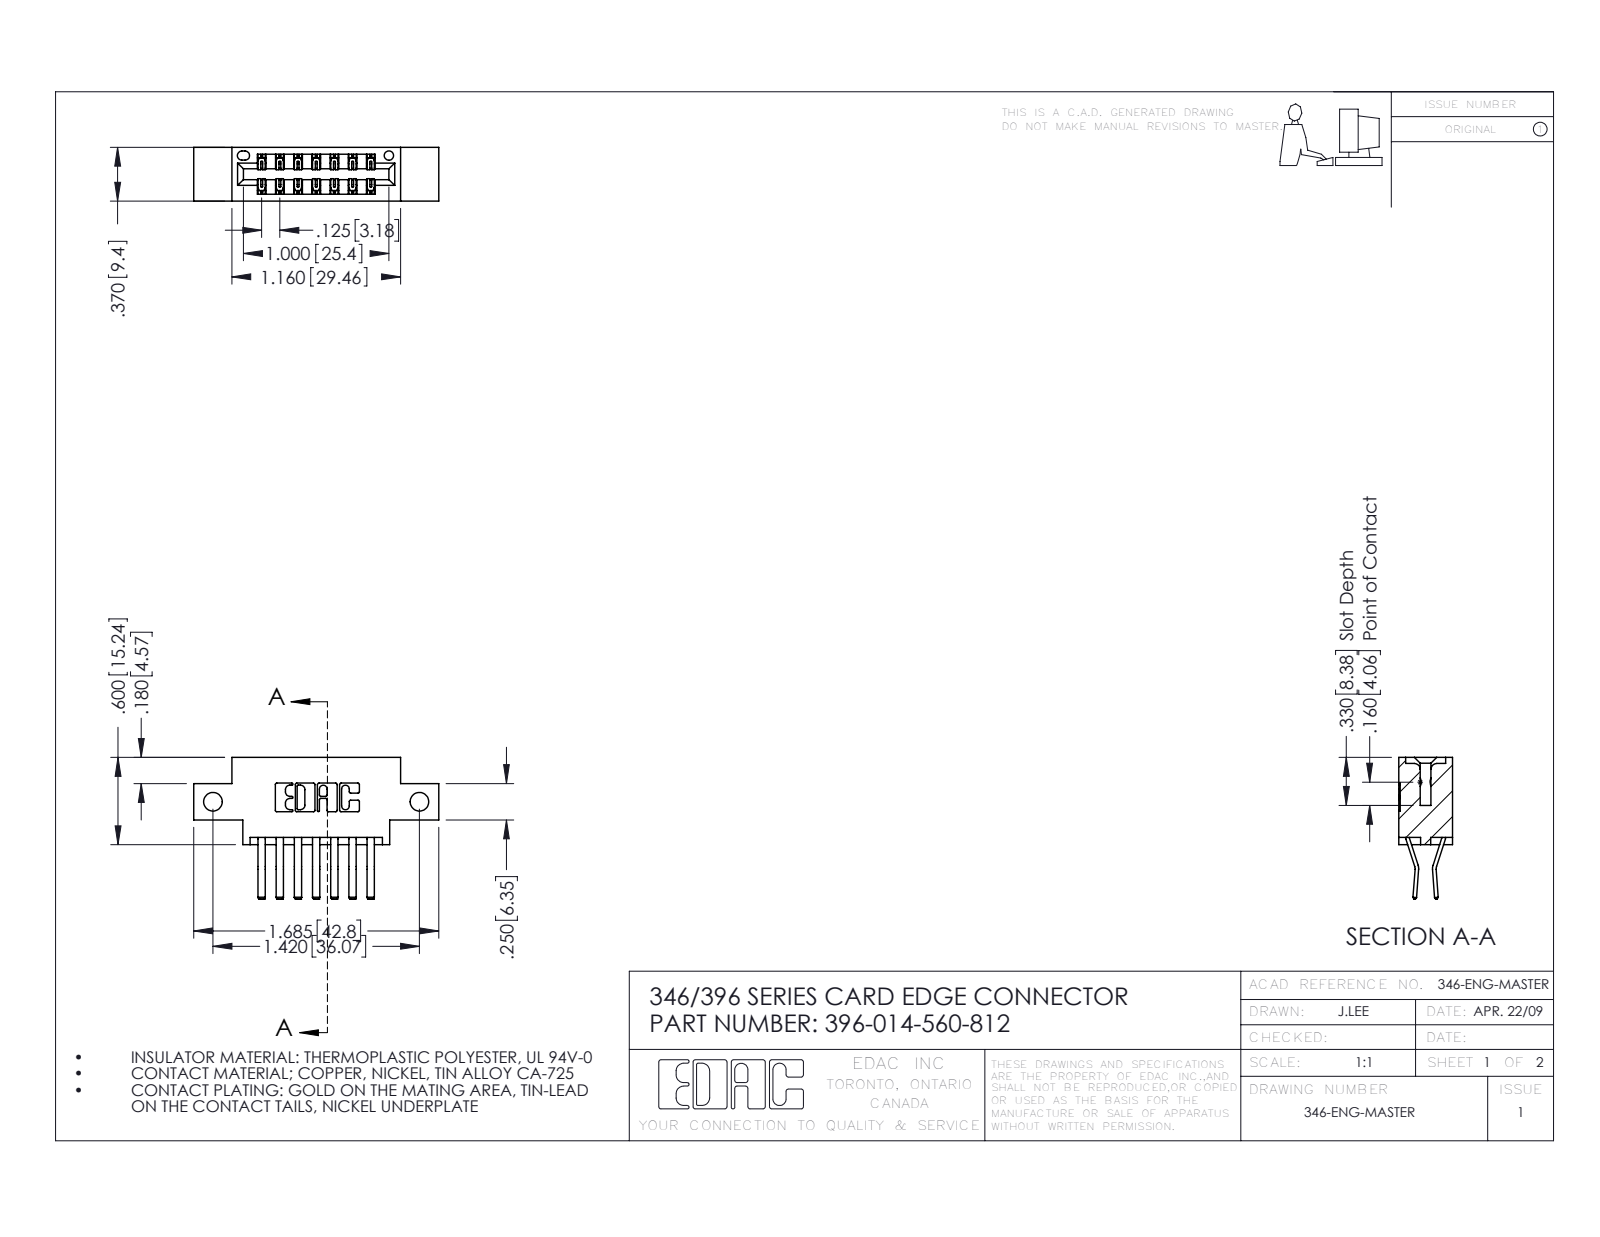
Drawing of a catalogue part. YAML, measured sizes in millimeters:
part_name: "346 Part_0.170 Offset - Side Mount; 396-014-560-812; 345-292-001_560 Tail"
step_written_by: "SolidWorks 2016 (CONFIG_CONTROL_DESIGN)"
units: millimeters
bodies: {solids: 15, faces: 882, planar: 570, cylindrical: 312, other: 0}
overall_size: [42.8, 24.8, 9.4]
volume: 3750
surface_area: 4894
round_holes:
  - {diameter: 3.3, count: 2}
  - {diameter: 1.6, count: 1}
partial_cylinders:
  - {radius: 0.3, count: 22}
  - {radius: 0.2, count: 21}
  - {radius: 0.2, count: 6}
  - {radius: 0.8, count: 6}
  - {radius: 0.7, count: 3}
  - {radius: 0.3, count: 2}
  - {radius: 0.4, count: 2}
  - {radius: 0.6, count: 2}
face_to_face_distances: [6.4, 9.4, 1.2, 8.2, 0.6, 3.8, 5.6, 2.5, 4.4, 1.8]
hole_center_spacings: [36.1]
